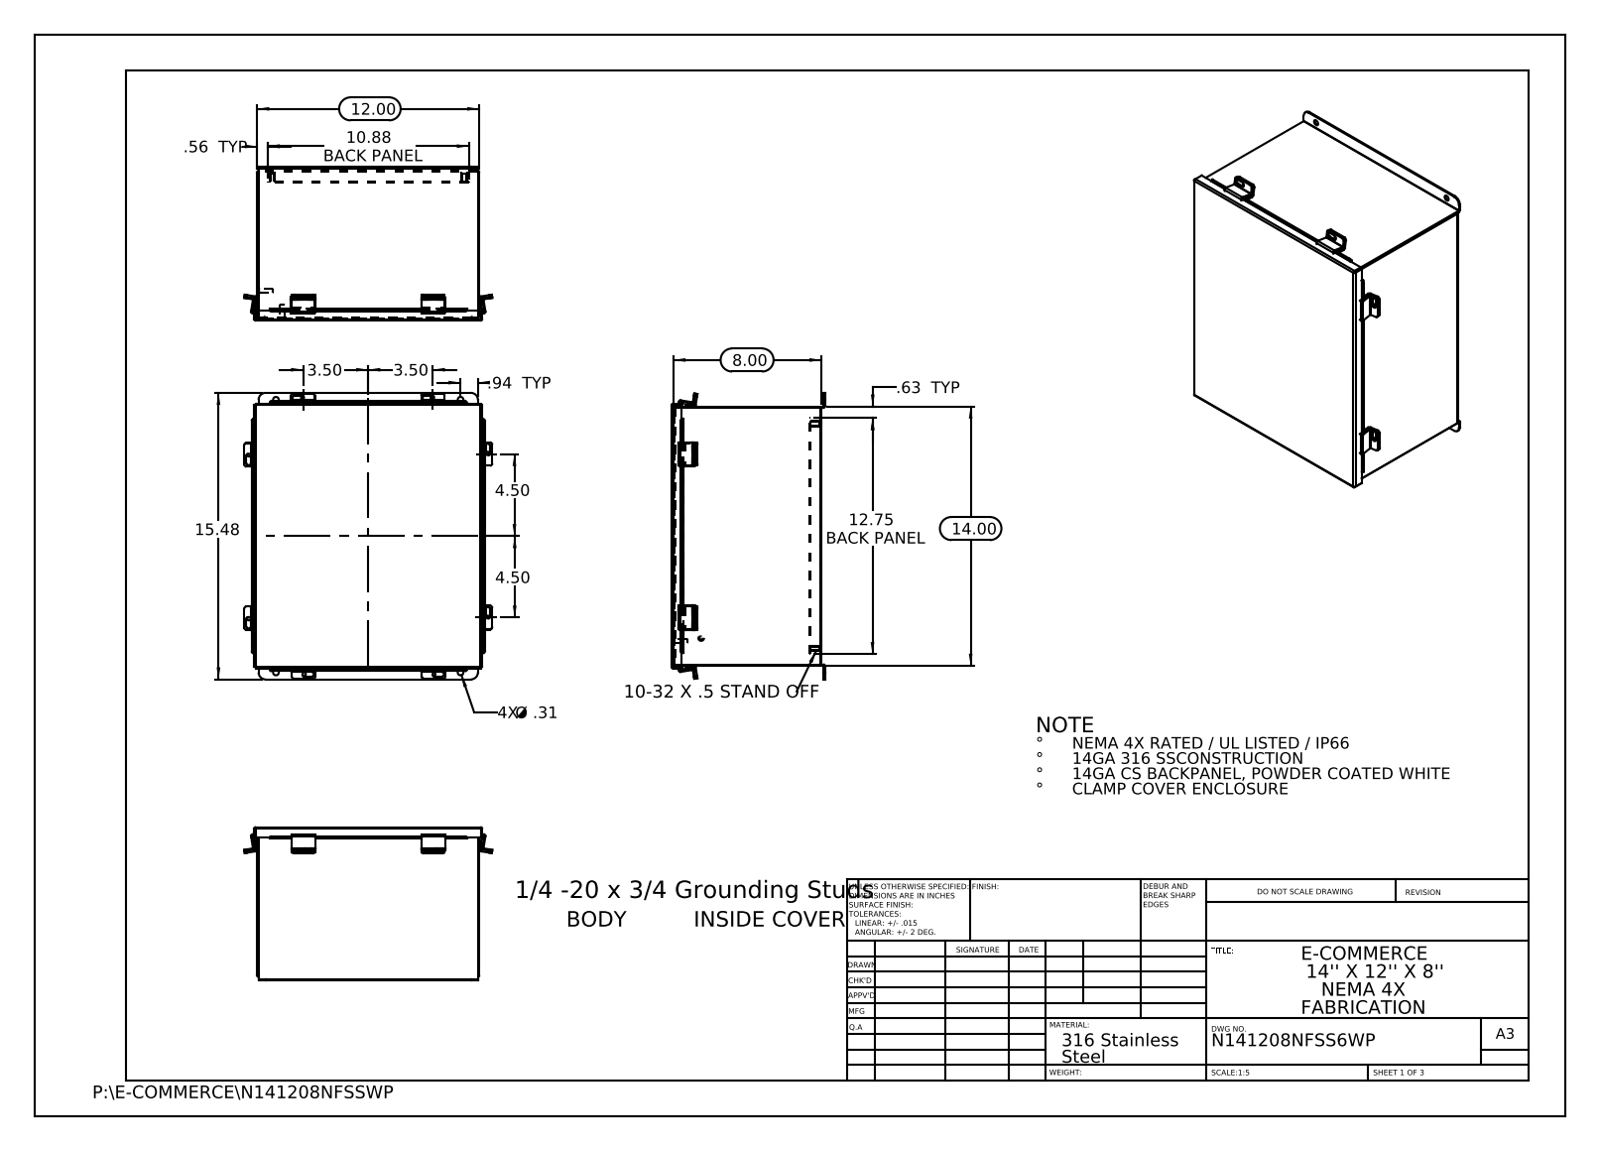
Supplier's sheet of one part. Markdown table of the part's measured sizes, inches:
| quantity | value |
| --- | --- |
| part name | N141208NFSSWP JIC_Cover_Template; N141208NFSSWP; N141208NFSSWP JIC Enclosure Template; N141208NFSSWP JIC_Standoff (+8 more) |
| STEP written by | SolidWorks 2013 (CONFIG_CONTROL_DESIGN) |
| units | inches |
| bodies | 27 solids, 806 faces (519 planar, 267 cylindrical, 20 other) |
| overall size | 15.476 × 13.072 × 8.39 |
| volume | 75.19 in³ |
| surface area | 2 046 in² |
| round holes (diameter × count) | 0.25 × 10, 0.187 × 4, 0.312 × 4, 0.125 × 1, 0.125 × 1, 0.373 × 1, 0.375 × 1 |
| round bosses / shafts (diameter × count) | 0.313 × 4, 0.315 × 2, 0.236 × 2, 0.273 × 1, 0.25 × 1 |
| partial cylindrical surfaces (radius × count) | 0.125 × 21, 0.013 × 13, 0.009 × 12, 0.088 × 12, 0.133 × 12, 0.083 × 6, 0.1 × 6, 0.375 × 4 |
| main face-to-face distances | 0.075, 8.128, 11.925, 13.925, 8.053, 8.203, 0.575, 0.5, 7.553, 7.628 |
| hole center spacings | 1.315, 10.258, 13.428, 16.846, 7, 9.976, 10.375, 12.126 |
